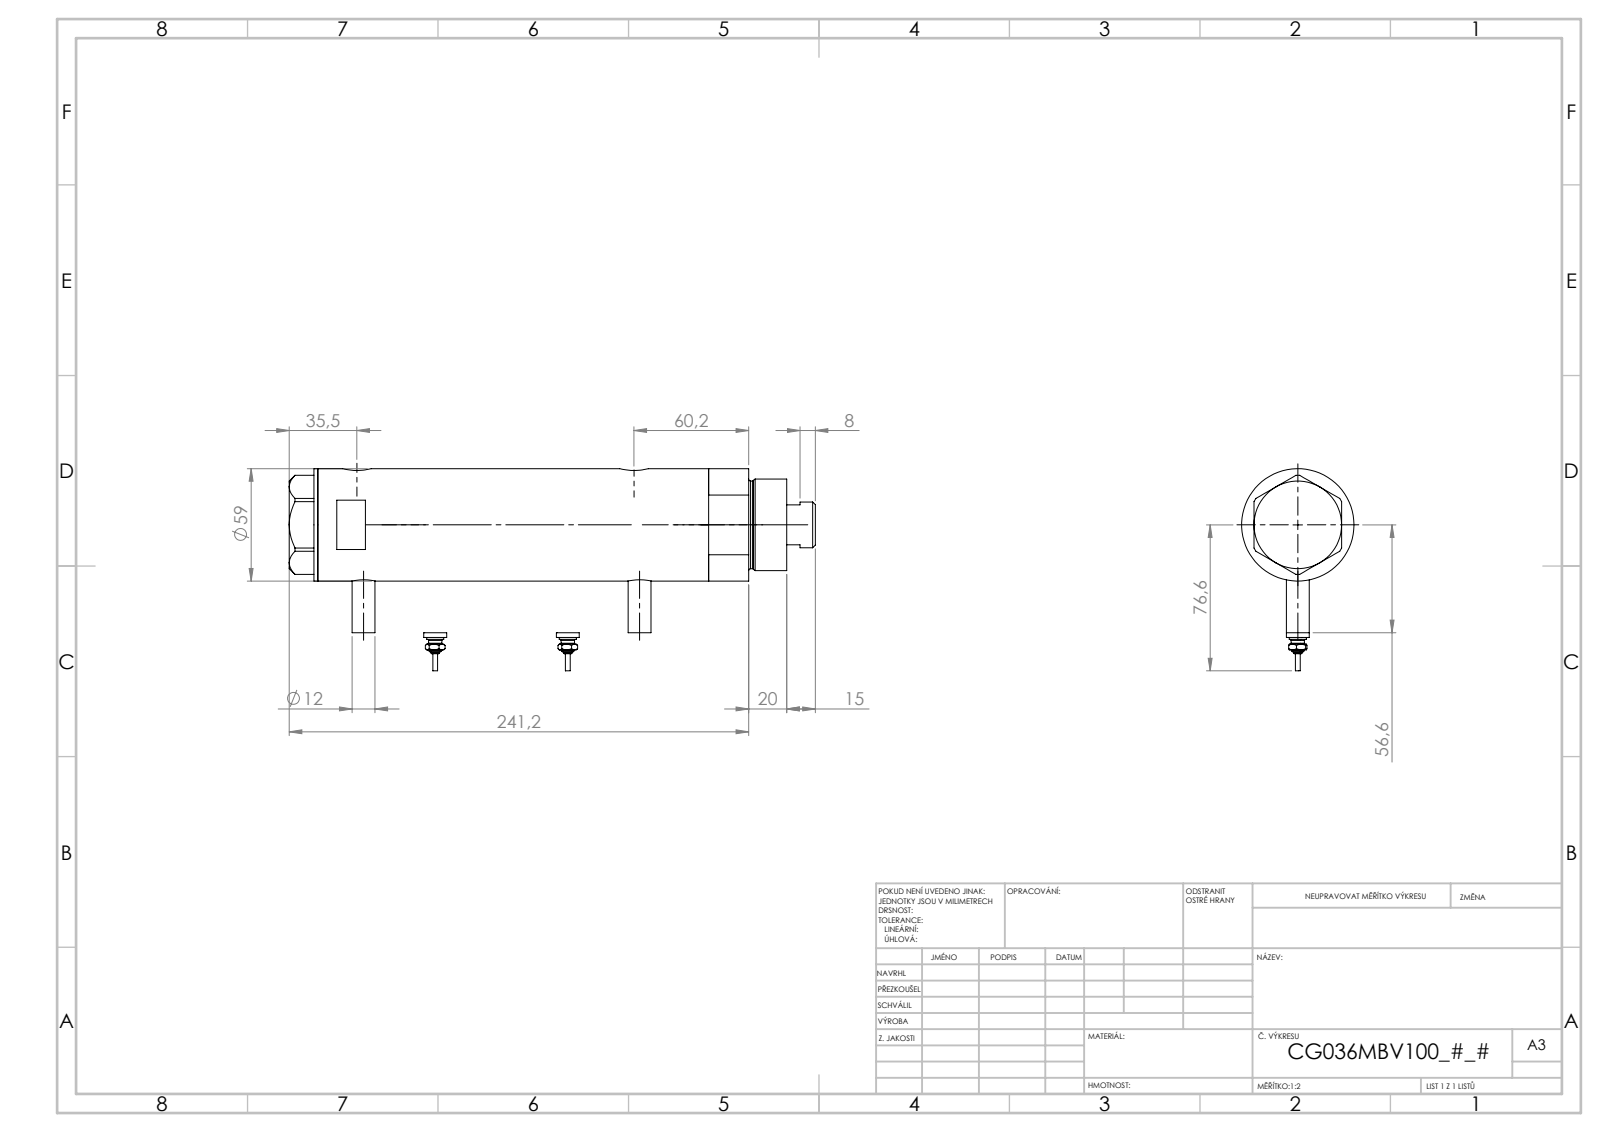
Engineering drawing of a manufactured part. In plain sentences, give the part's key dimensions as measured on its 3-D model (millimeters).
The part is named "V270CG_VC; V270CG_FRONT; V270CG_SWITCH; V270CG_BACK (+1 more)". Its 3-D file was written by "SolidWorks 2019 (CONFIG_CONTROL_DESIGN)". It is 6 solids with 232 faces: 81 planar, 77 cylindrical and 74 other. Overall it measures 263.42 by 91.3 by 59 millimeters. Its volume is 594 695 cubic millimeters and its surface area 121 539 square millimeters. Round holes: 2 of diameter 5, 2 of diameter 9.73, 2 of diameter 12.5, 2 of diameter 15, 1 of diameter 8.5, 1 of diameter 25, 1 of diameter 26.5, 1 of diameter 36, 1 of diameter 40, 1 of diameter 52. Round bosses or shafts: 4 of diameter 12, 2 of diameter 9, 2 of diameter 7, 2 of diameter 4.34, 2 of diameter 2.4, 1 of diameter 59, 1 of diameter 48, 1 of diameter 46. The main face-to-face distances are 157.34, 23.5, 133.84, 15, 38.5, 172.34, 248.42, 233.42, 209.92, 76.08. The hole center spacings are 2.9, 3.5, 132.15, 135.05, 135.65, 138.55, 2.89, 2.91.
